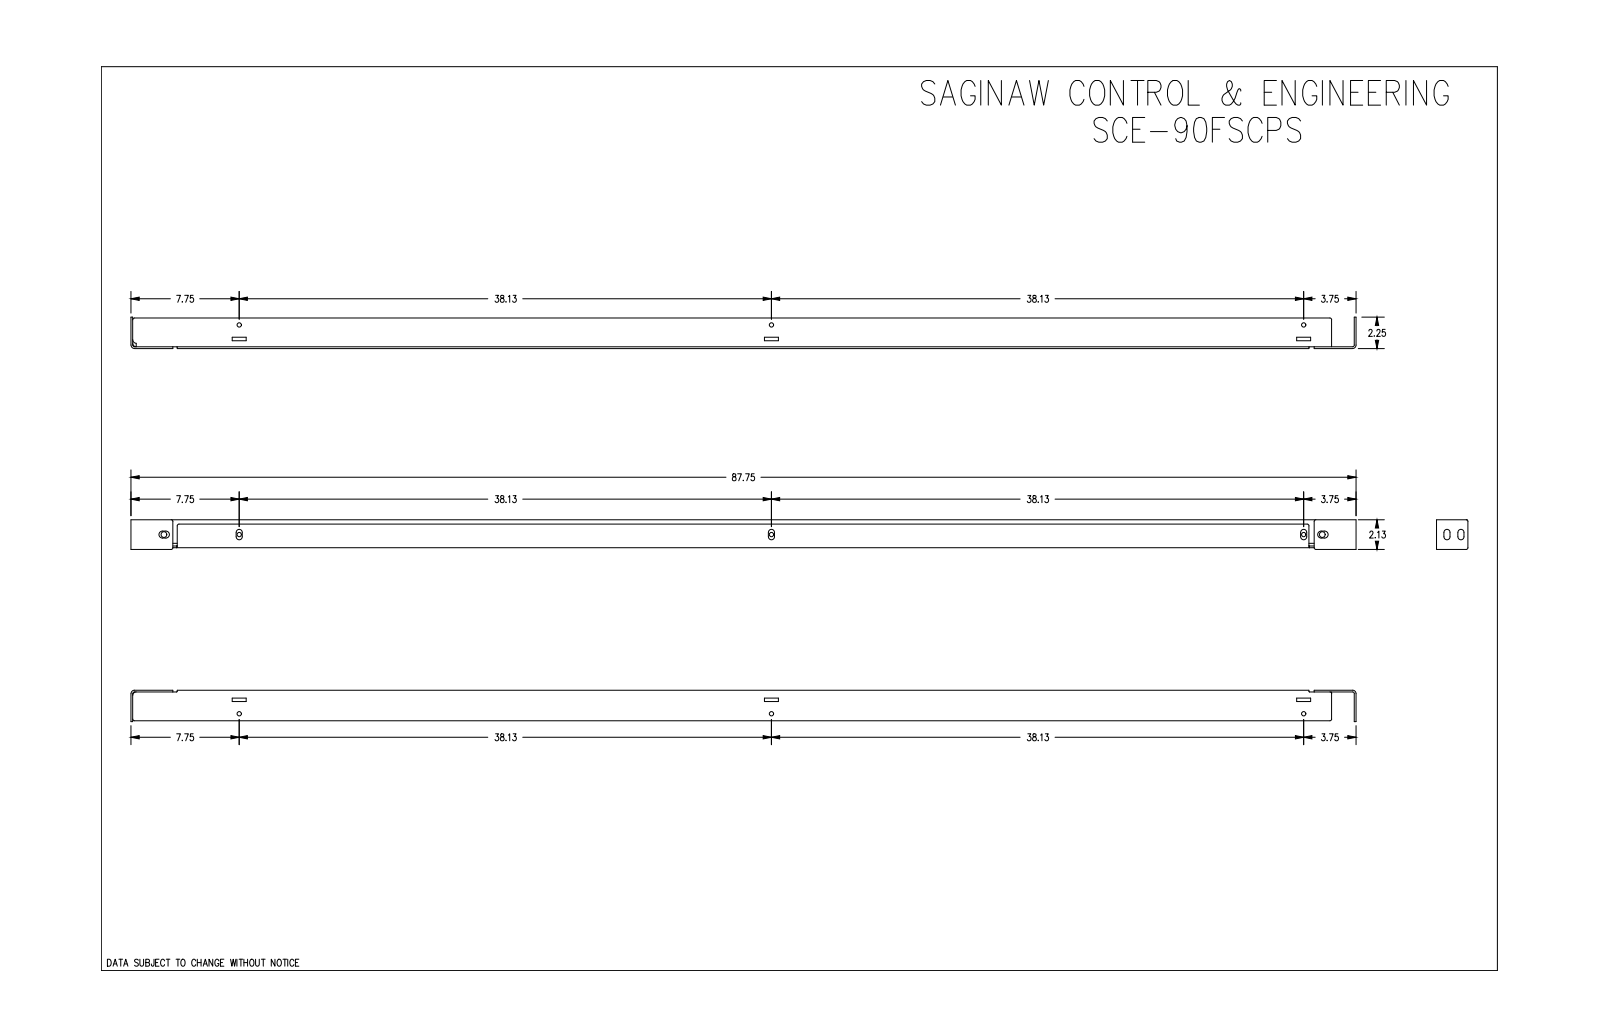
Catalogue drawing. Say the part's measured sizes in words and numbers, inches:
The part is named "SCE-90FSCPS". Its 3-D file was written by "SolidWorks 2019 (CONFIG_CONTROL_DESIGN)". It is 4 solids with 141 faces: 79 planar, 56 cylindrical and 6 other. Overall it measures 87.75 by 2.25 by 2.125 inches. Its volume is 78.45 cubic inches and its surface area 1 309 square inches. Round holes: 6 of diameter 0.312, 2 of diameter 0.406. Partial cylindrical surfaces (rounded edges, fillets, slot ends): 17 of radius 0.125, 10 of radius 0.25, 6 of radius 0.219, 4 of radius 0.219. The main face-to-face distances are 0.125, 0.125, 2, 1.875, 1.75, 1.875, 0.25, 0.313, 2.187, 2.062. The hole center spacings are 38.125, 38.125, 76.25, 1.328, 5.39, 39.453, 43.515, 77.578.
